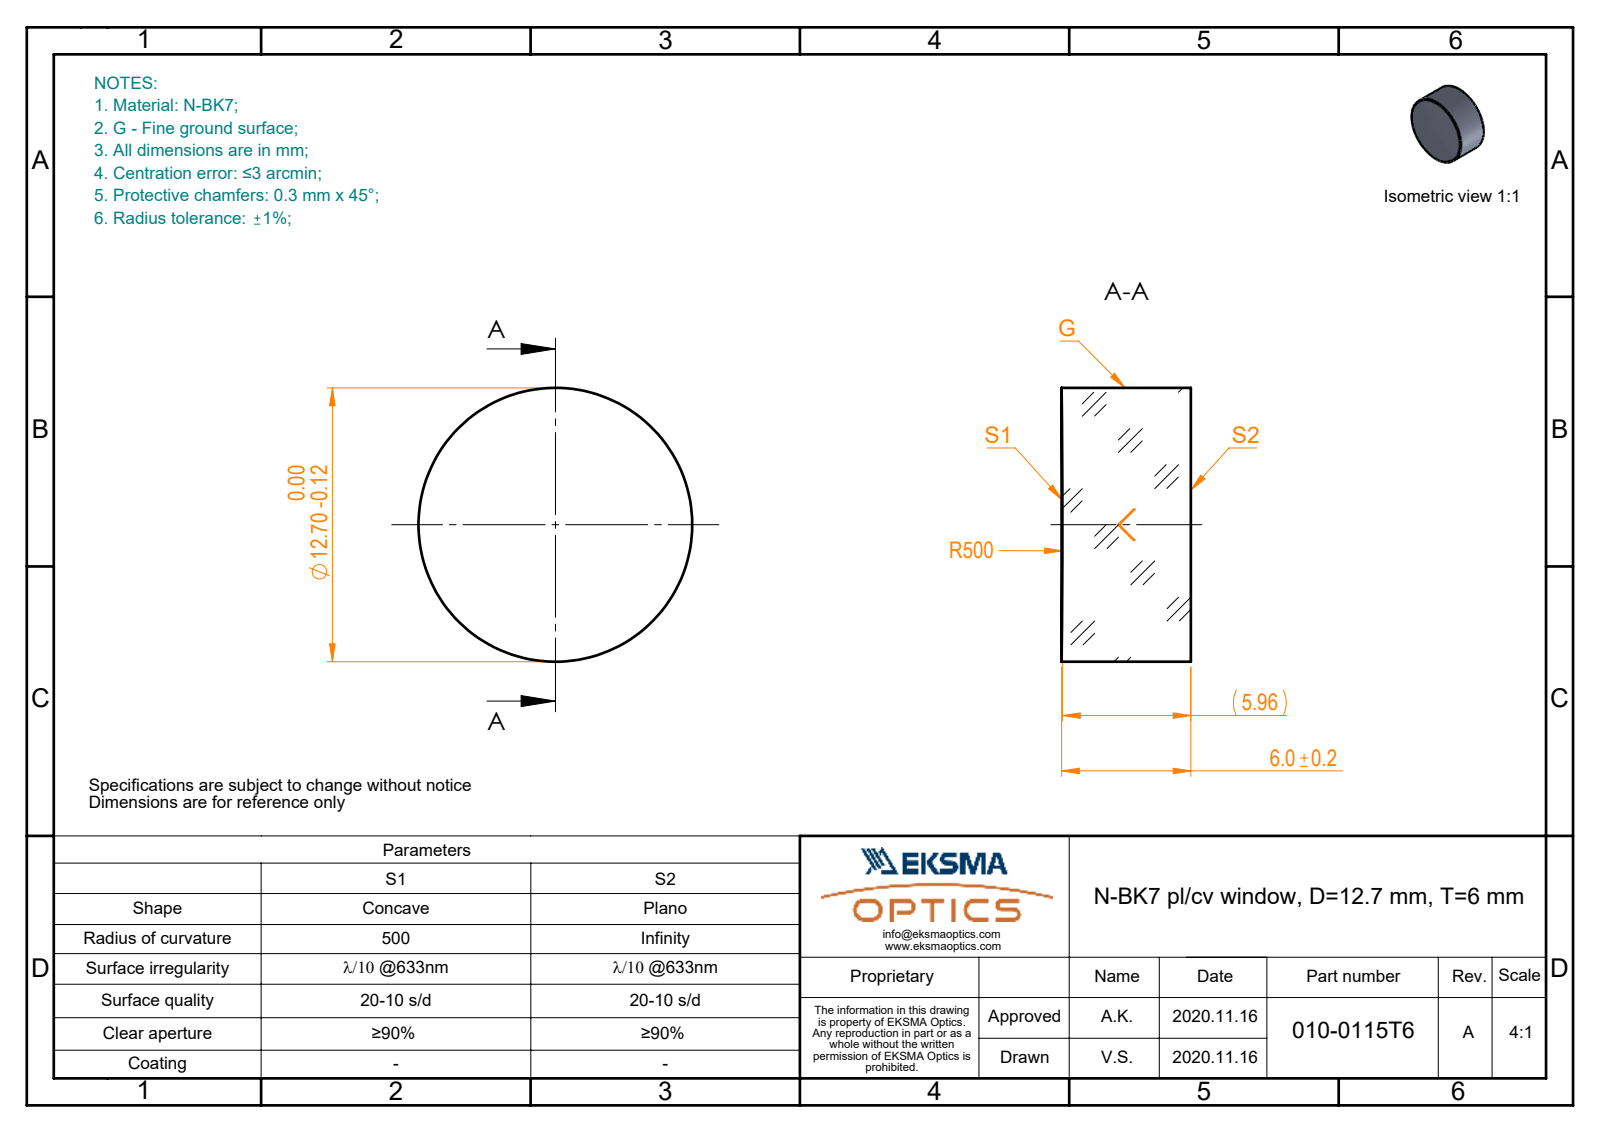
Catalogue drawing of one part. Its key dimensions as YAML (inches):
part_name: "010-0115T6_N-BK7_PCV_window"
step_written_by: "SolidWorks 2019 (CONFIG_CONTROL_DESIGN)"
units: inches
bodies: {solids: 1, faces: 5, planar: 1, cylindrical: 2, other: 2}
overall_size: [0.5, 0.5, 0.236]
volume: 0.046
surface_area: 0.764
round_bosses_or_shafts:
  - {diameter: 0.5, count: 1}
